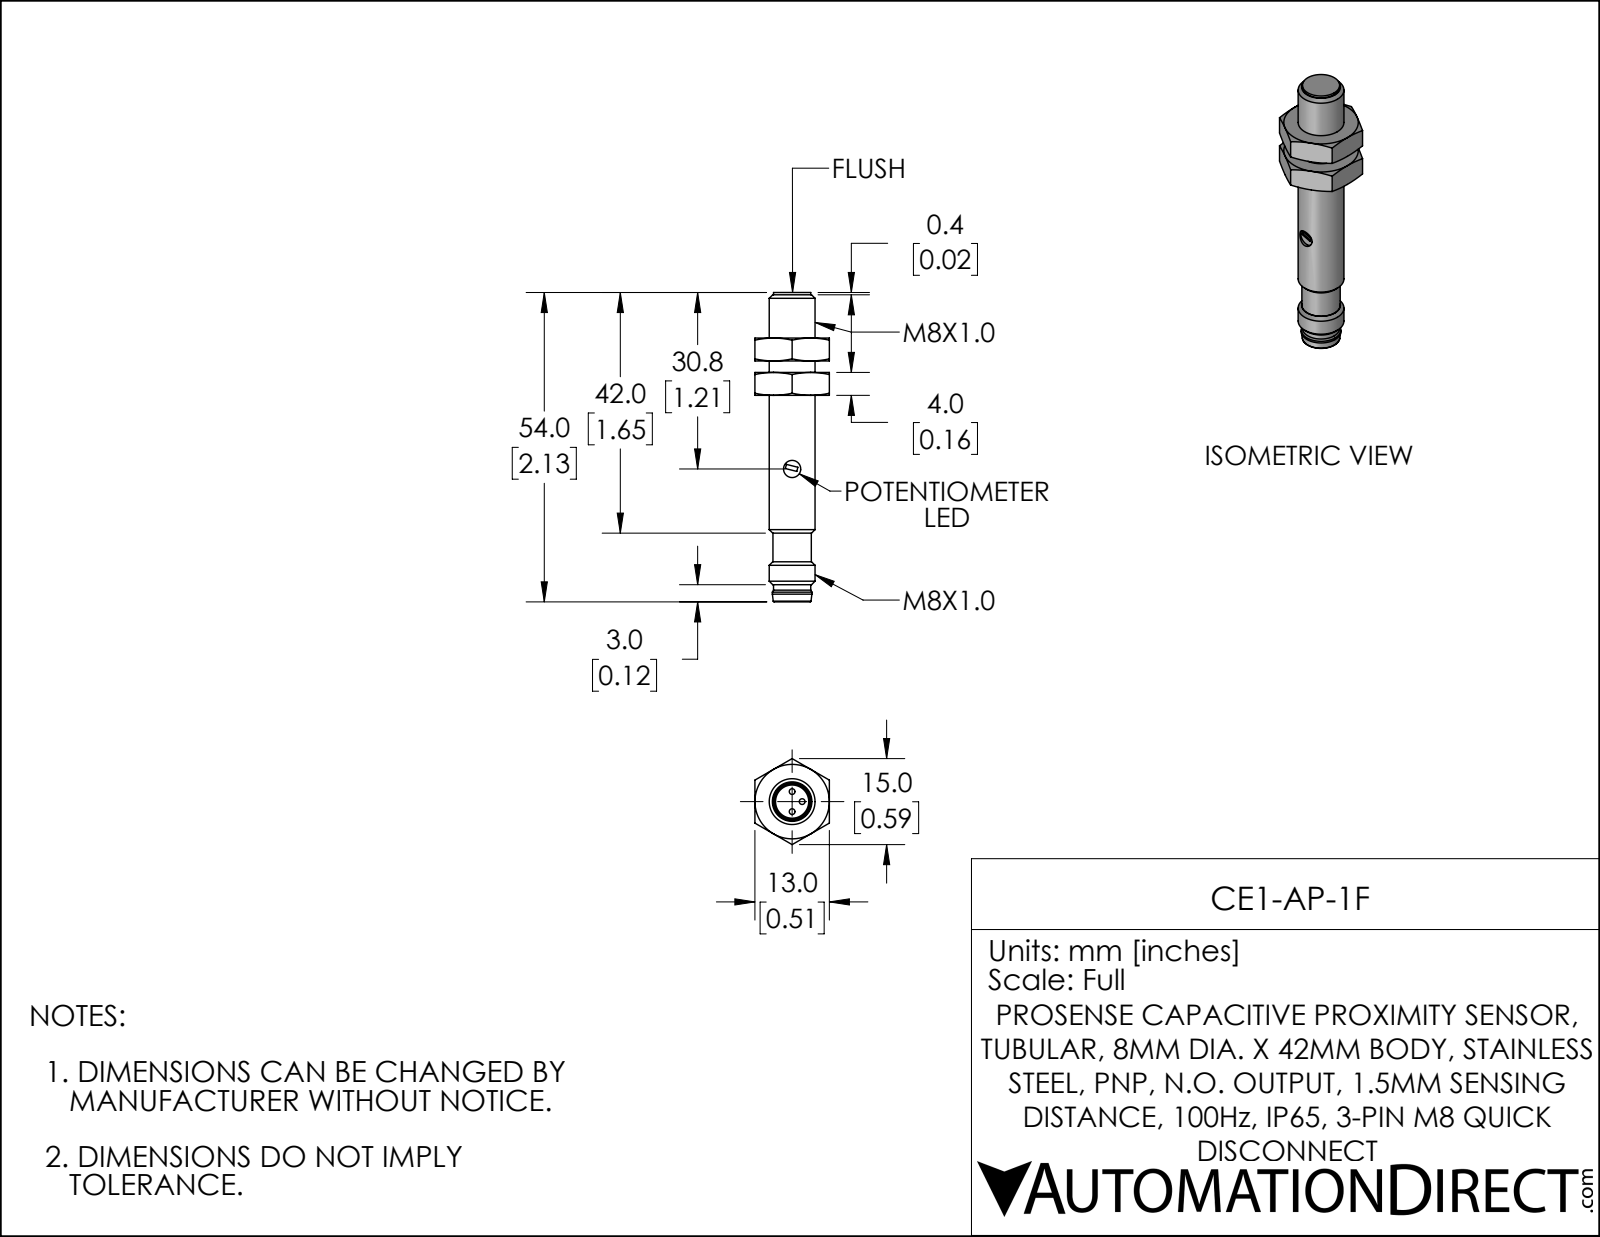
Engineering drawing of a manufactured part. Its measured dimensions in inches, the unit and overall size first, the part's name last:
Units: inches
Overall size (bounding box): 2.126 × 0.591 × 0.512
Round holes (diameter × count): ⌀0.118 ×1, ⌀0.228 ×1, ⌀0.272 ×1
Round bosses / shafts (diameter × count): ⌀0.039 ×3, ⌀0.315 ×1, ⌀0.272 ×1, ⌀0.264 ×1, ⌀0.256 ×1
Main face-to-face distances: 0.512, 0.157, 0.236, 0.079, 0.394, 0.313, 0.47, 0.549, 0.707, 1.459
Volume: 0.201 in³ · Surface area: 3.838 in²
Bodies: 3 solids, 80 faces (31 planar, 13 cylindrical, 36 other)
Part name (STEP PRODUCT): CE1-AP-1F
STEP written by: SolidWorks 2019 (CONFIG_CONTROL_DESIGN)
